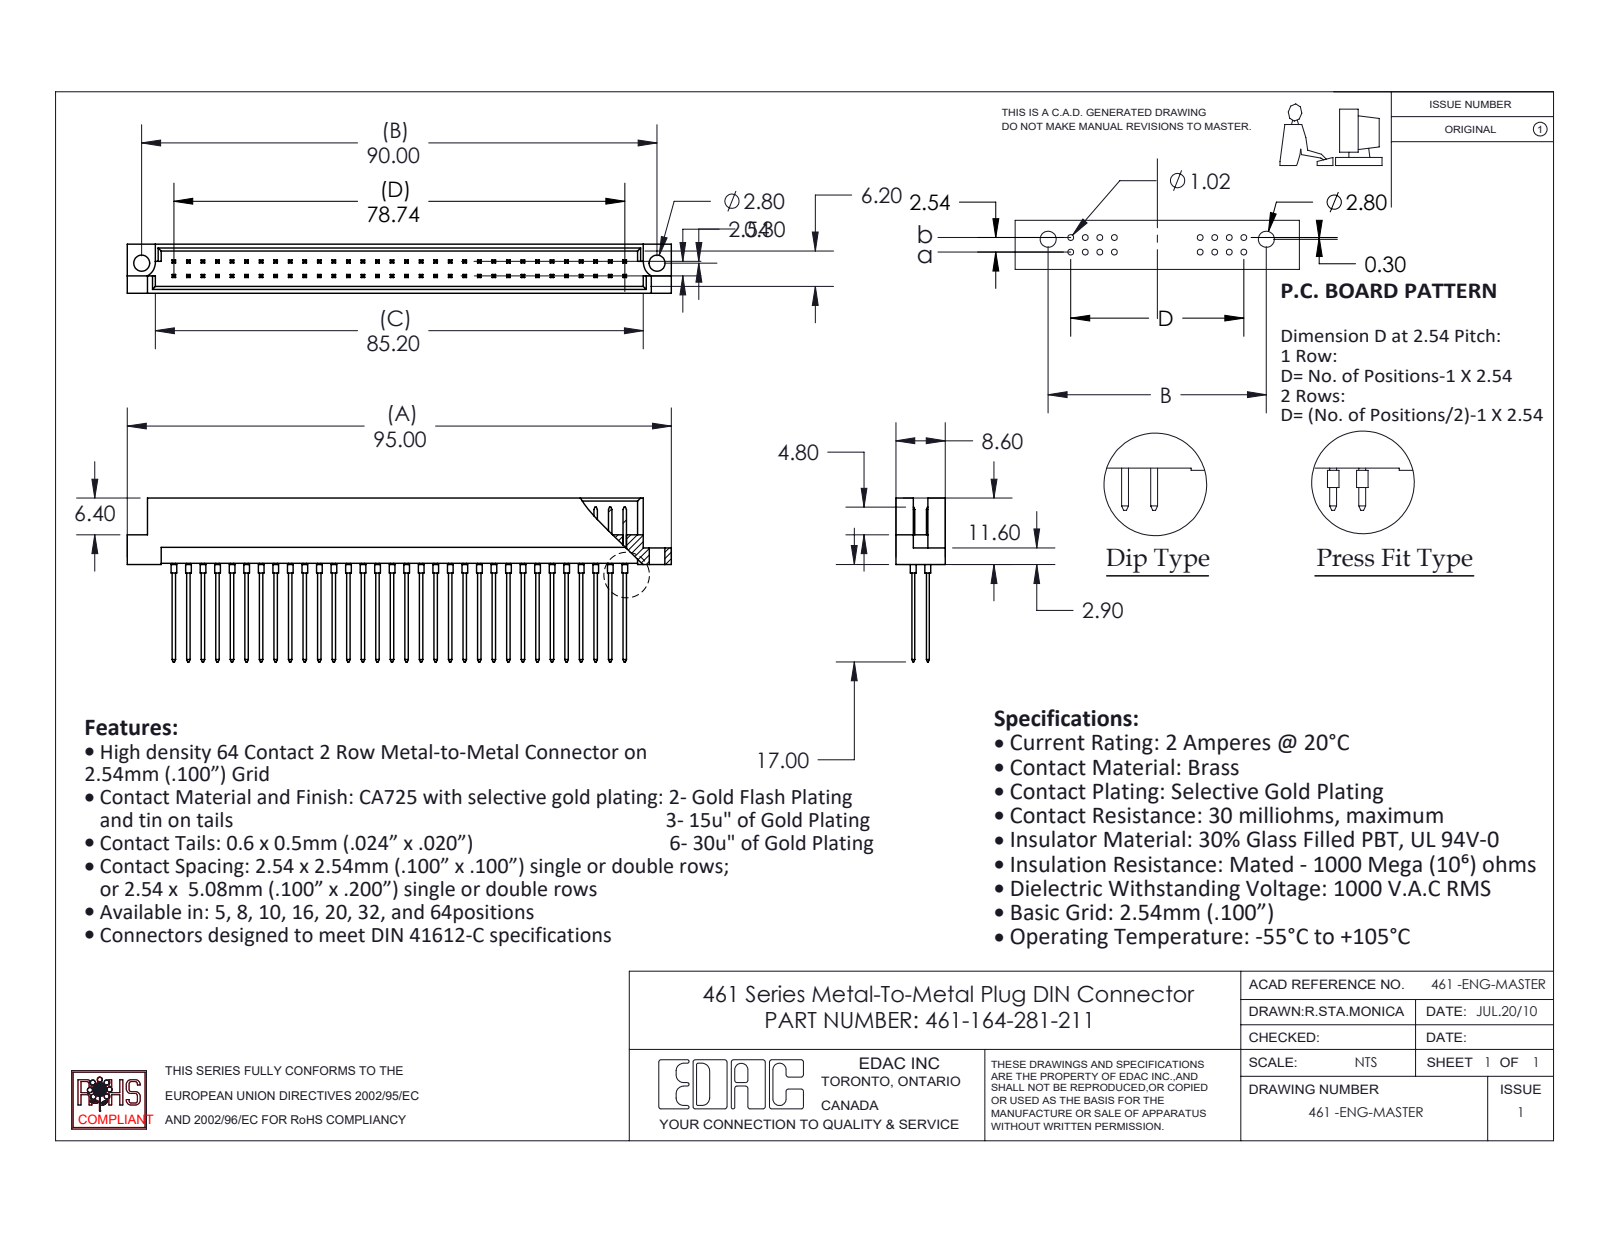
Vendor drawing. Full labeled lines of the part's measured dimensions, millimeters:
Part name (STEP PRODUCT): 461-290_81; 461 Part_64; 461-164-281-211
STEP written by: SolidWorks 2020 (CONFIG_CONTROL_DESIGN)
Units: millimetres
Bodies: 65 solids, 1713 faces (1578 planar, 135 cylindrical, 0 other)
Overall size (bounding box): 95 × 28.6 × 8.6
Volume: 5 214 mm³ · Surface area: 9 601 mm²
Round holes (diameter × count): ⌀2.8 ×2
Round bosses / shafts (diameter × count): ⌀1 ×64
Partial cylindrical surfaces — rounded edges, fillets, slot ends (radius × count): R2.8 ×2
Main face-to-face distances: 2.54, 1.2, 7.4, 3.28, 5.32, 2.08, 4.12, 2.78, 5.82, 1.58
Hole centre spacings: 90
